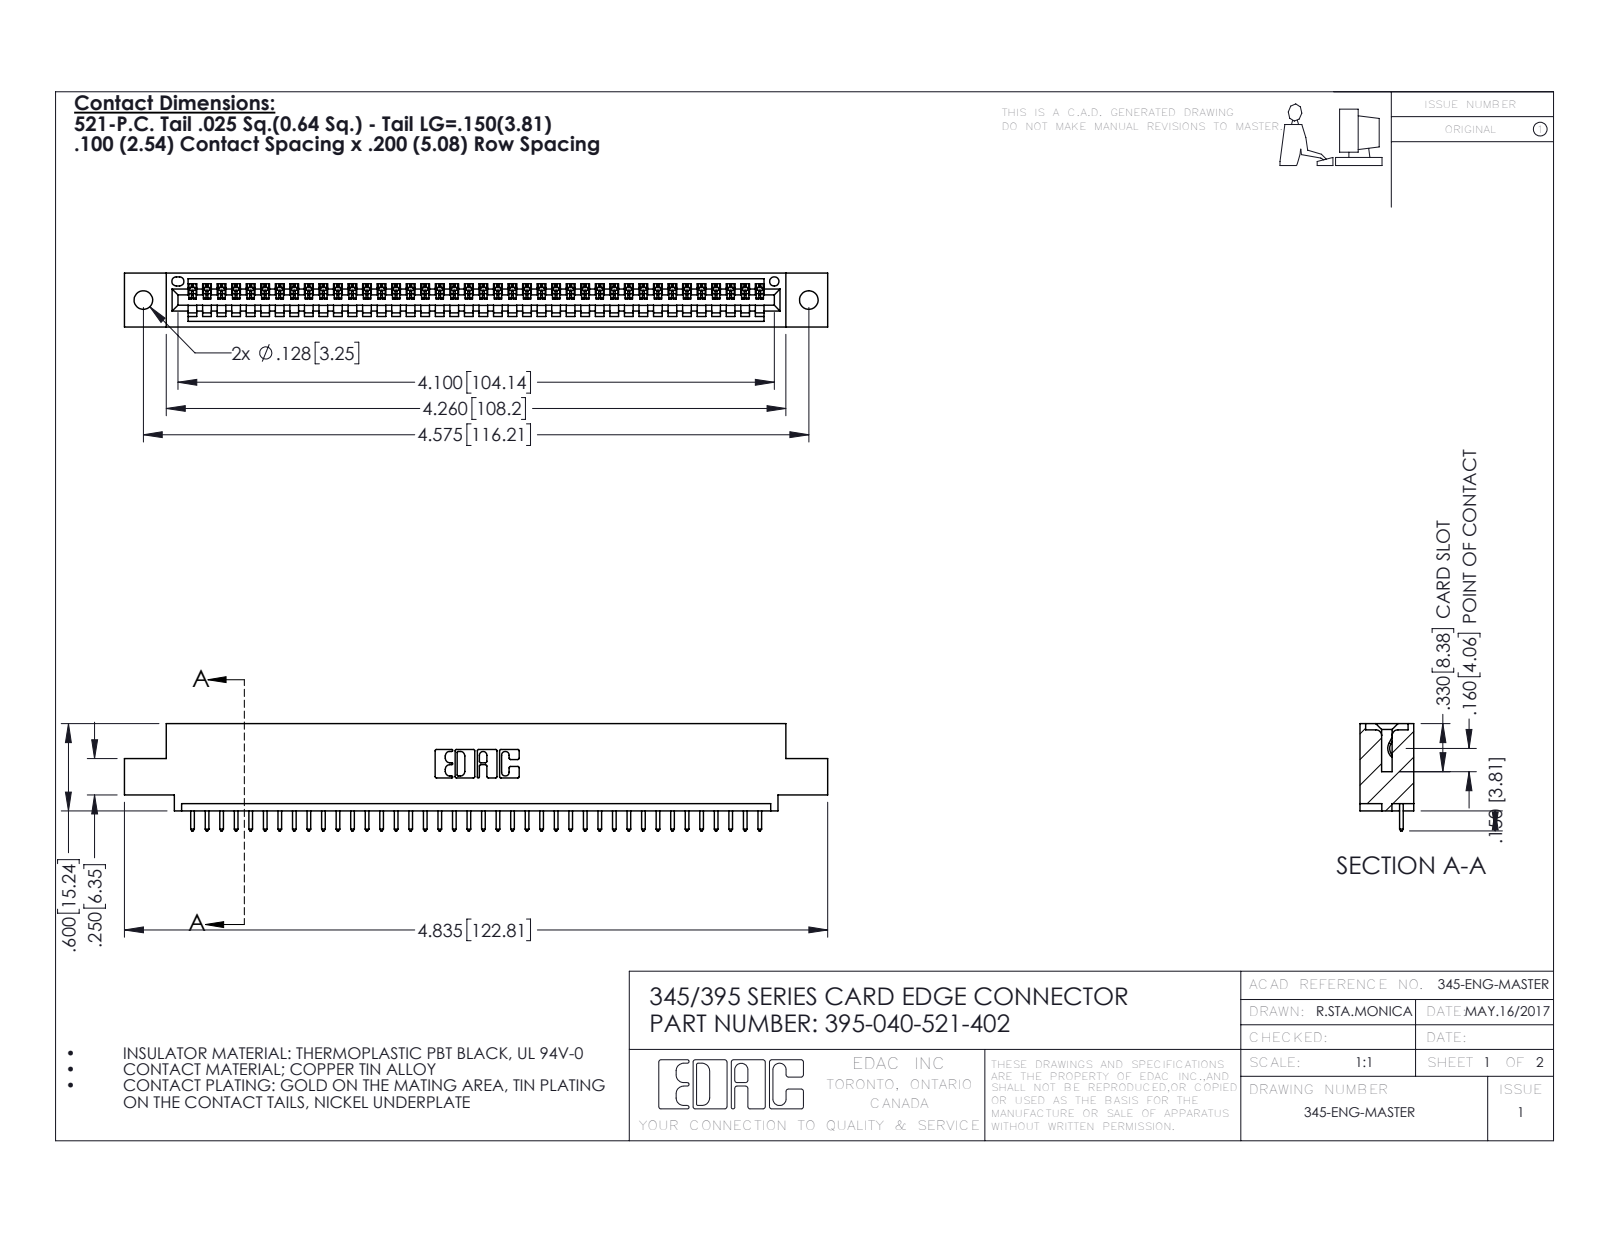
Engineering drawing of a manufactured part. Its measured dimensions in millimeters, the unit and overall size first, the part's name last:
Units: millimetres
Overall size (bounding box): 122.8 × 18.7 × 9.4
Round holes (diameter × count): ⌀3.3 ×2, ⌀1.6 ×1
Partial cylindrical surfaces — rounded edges, fillets, slot ends (radius × count): R0.2 ×80, R0.3 ×80, R0.3 ×22, R0.2 ×6, R0.8 ×6, R0.7 ×3, R0.8 ×2, R1 ×2
Main face-to-face distances: 7.6, 1.8, 9.4, 5.1, 2.5, 6.9, 0.6, 5.7, 3.8, 1.8
Hole centre spacings: 6.9, 110.2, 116.2
Volume: 11 400 mm³ · Surface area: 14 520 mm²
Bodies: 41 solids, 2450 faces (1684 planar, 766 cylindrical, 0 other)
Part name (STEP PRODUCT): 345 Part_0.110 Offset - 0.128 Dia; 345-292-001_345-293-121; 395-040-521-402
STEP written by: SolidWorks 2016 (CONFIG_CONTROL_DESIGN)
